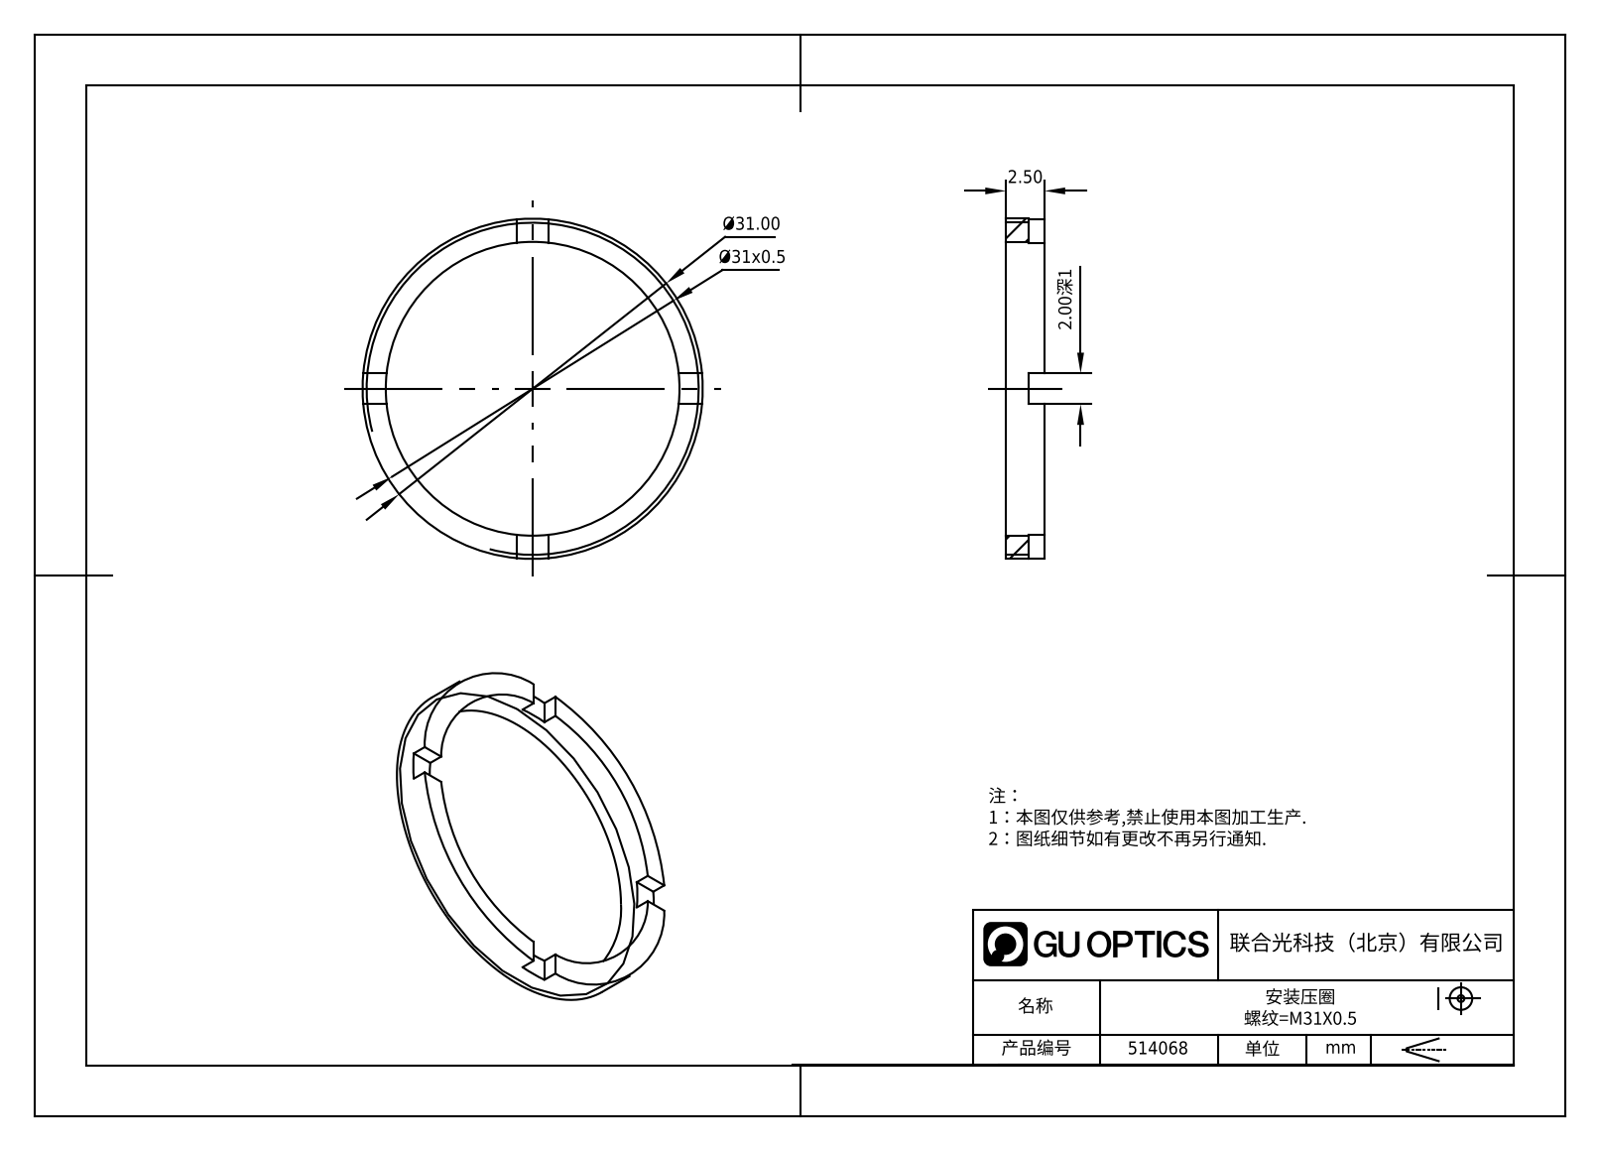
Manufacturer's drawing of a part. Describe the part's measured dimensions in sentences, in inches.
The part is named "514068". Its 3-D file was written by "SolidWorks 2020 (CONFIG_CONTROL_DESIGN)". It is 1 solid with 21 faces: 17 planar, 4 cylindrical and 0 other. Overall it measures 1.22 by 1.22 by 0.098 inches. Its volume is 0.027 cubic inches and its surface area 1.27 square inches. Round holes: 1 of diameter 1.063. Round bosses or shafts: 1 of diameter 1.22. The main face-to-face distances are 0.098, 0.059, 0.039, 0.079.
